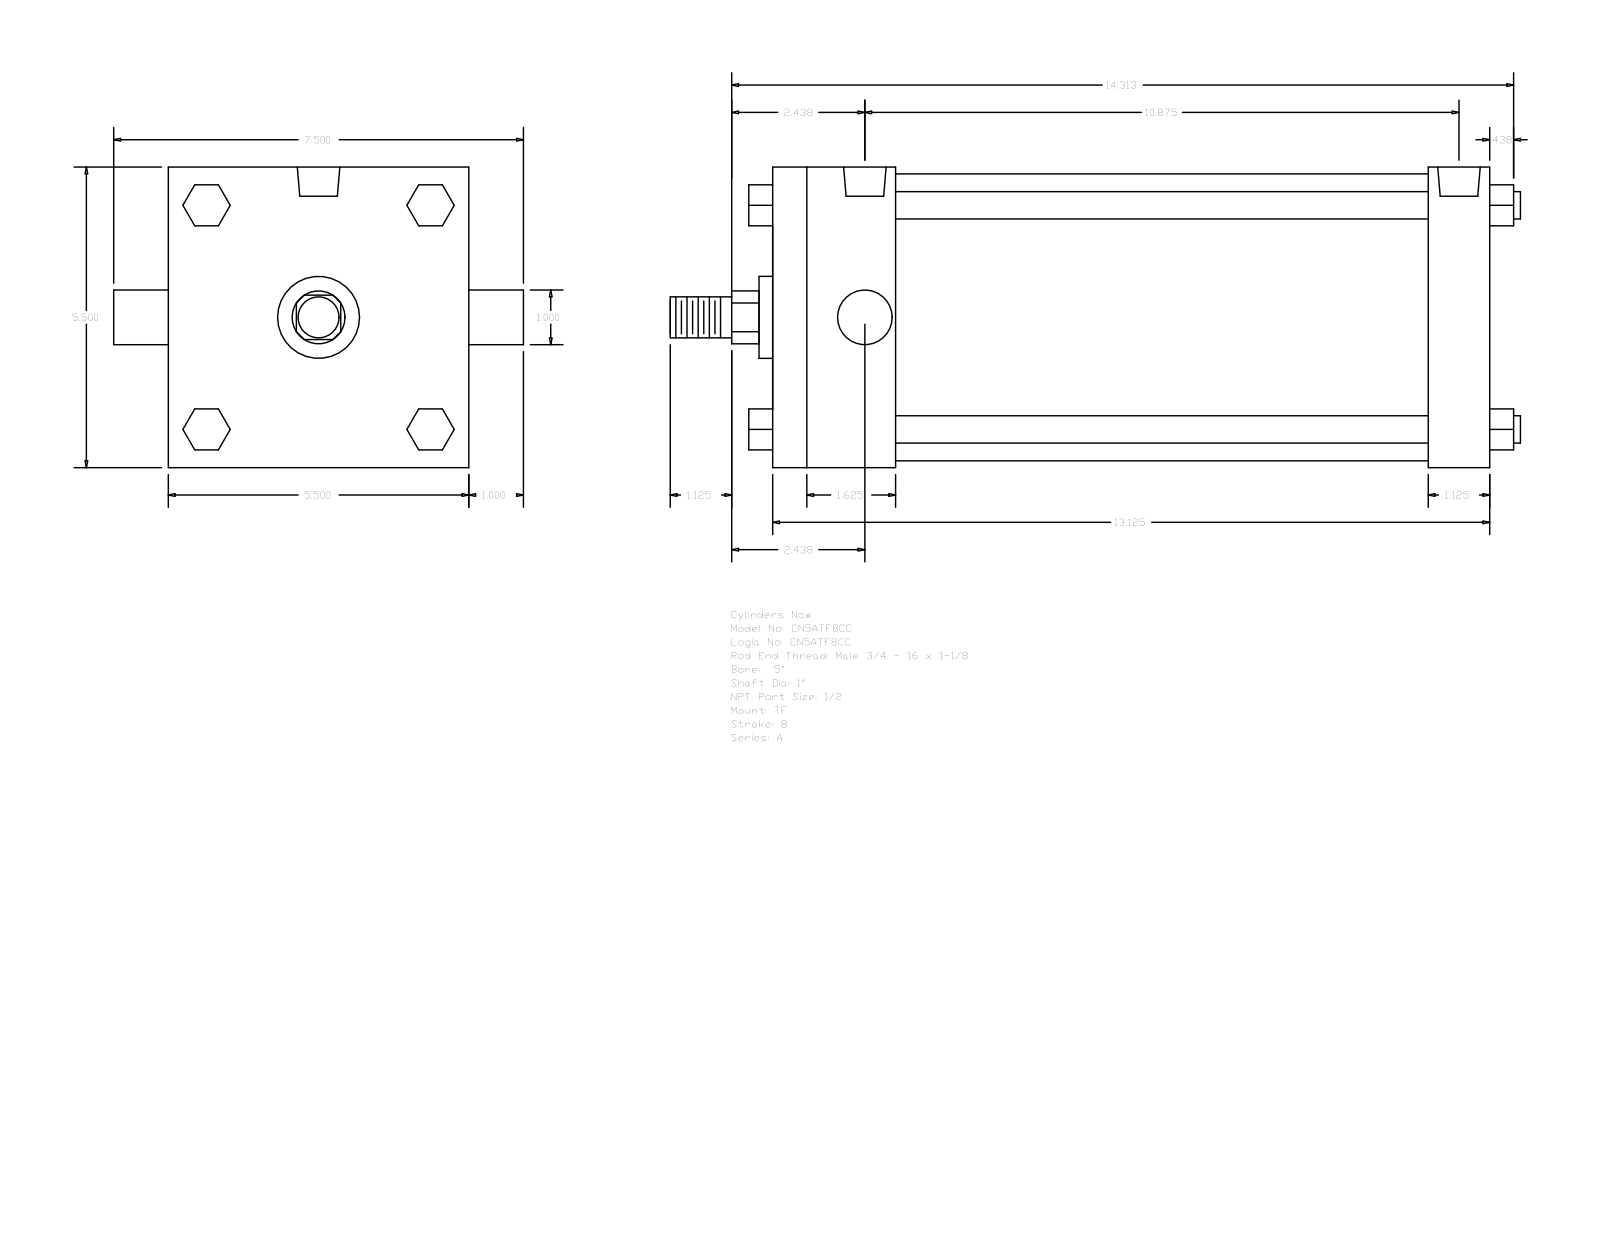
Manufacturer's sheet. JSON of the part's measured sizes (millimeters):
{"part_name": "A_TF__0500_1", "step_written_by": "GSSL Pune (CONFIG_CONTROL_DESIGN)", "units": "millimeters", "bodies": {"solids": 0, "faces": 120, "planar": 92, "cylindrical": 28, "other": 0}, "overall_size": [395.29, 190.5, 139.7], "round_holes": [[8.73, 3], [19.77, 2]], "round_bosses_or_shafts": [[12.7, 4], [25.4, 2], [133.35, 1], [38.1, 1], [19.05, 1]], "partial_cylinders_radius": [[12.29, 1]], "face_to_face_distances": [139.7, 333.38, 304.8, 28.58, 57.15, 247.65, 276.23, 19.05, 52.07, 90.18], "hole_center_spacings": [2.39, 273.84, 271.45, 276.23]}
